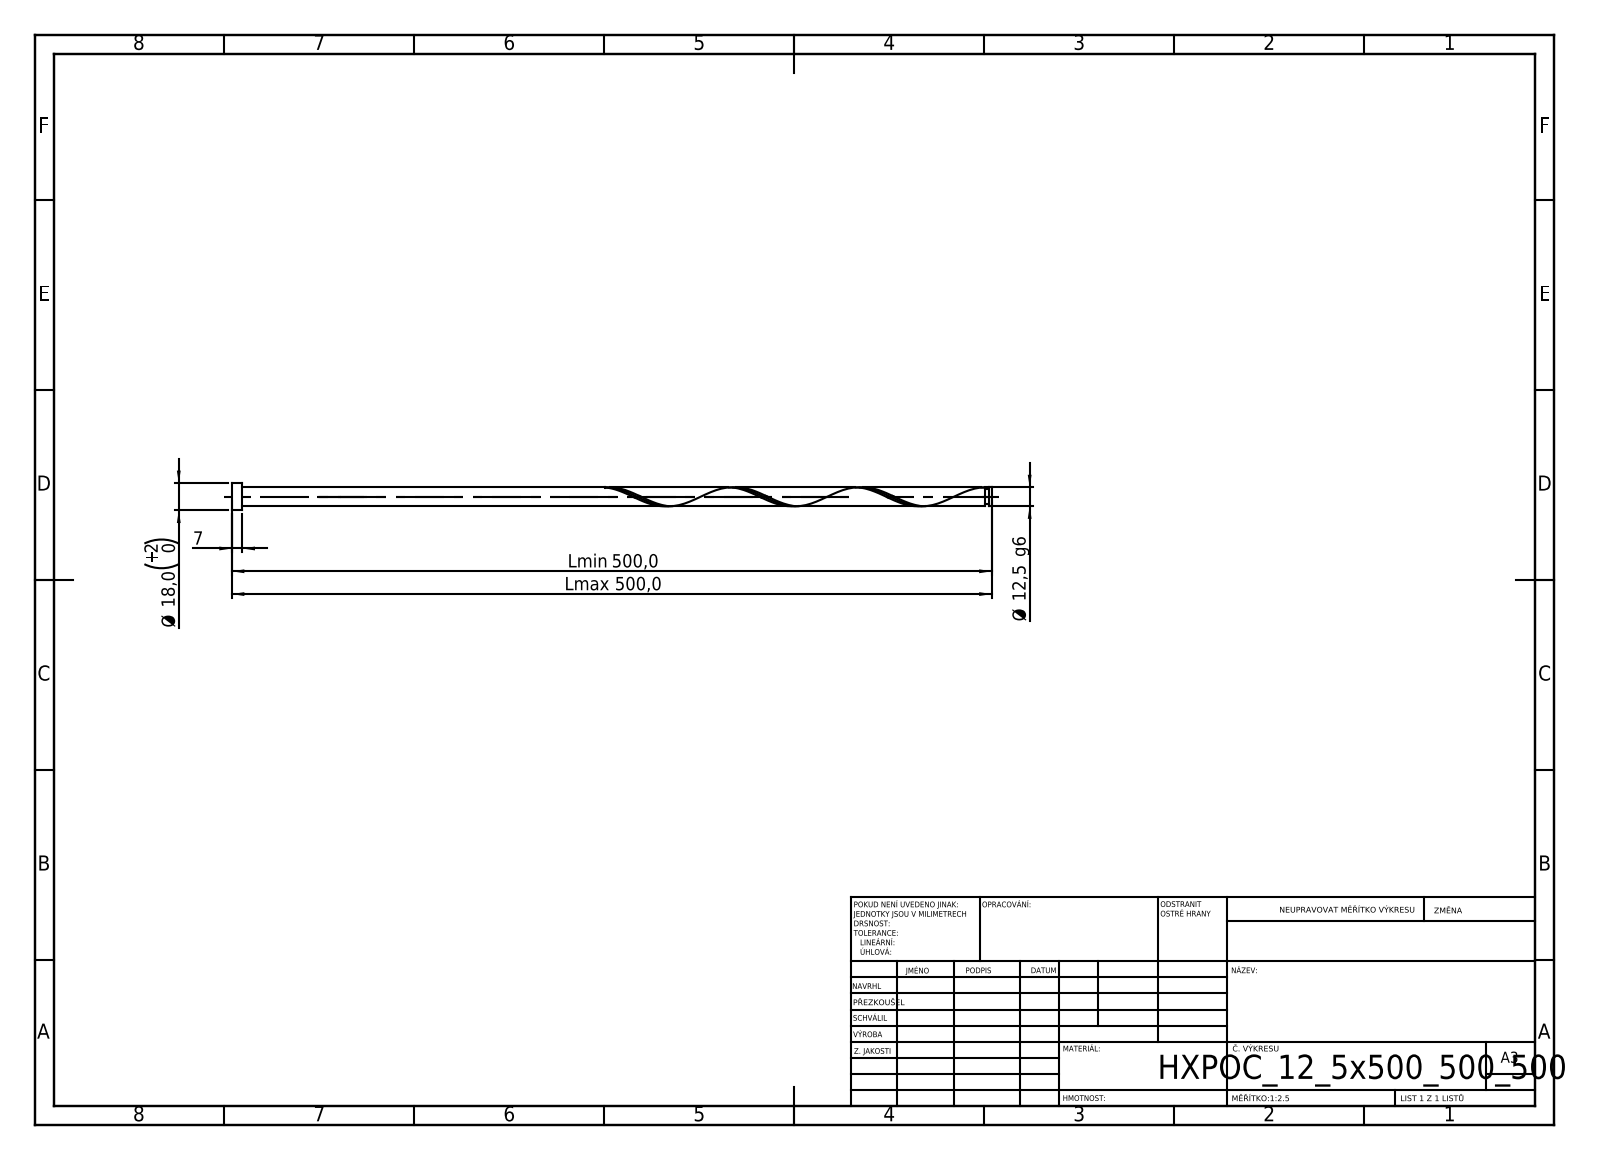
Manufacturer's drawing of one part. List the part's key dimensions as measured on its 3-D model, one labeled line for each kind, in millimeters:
STEP written by: SolidWorks 2019 (CONFIG_CONTROL_DESIGN)
Units: millimetres
Bodies: 1 solid, 21 faces (6 planar, 14 cylindrical, 1 other)
Overall size (bounding box): 500 × 18 × 18
Volume: 61 584 mm³ · Surface area: 20 673 mm²
Round bosses / shafts (diameter × count): ⌀18 ×1, ⌀12.5 ×1, ⌀10 ×1
Main face-to-face distances: 7, 500, 493, 498.37, 491.37, 1.63, 495.87, 488.87, 2.5, 4.13
